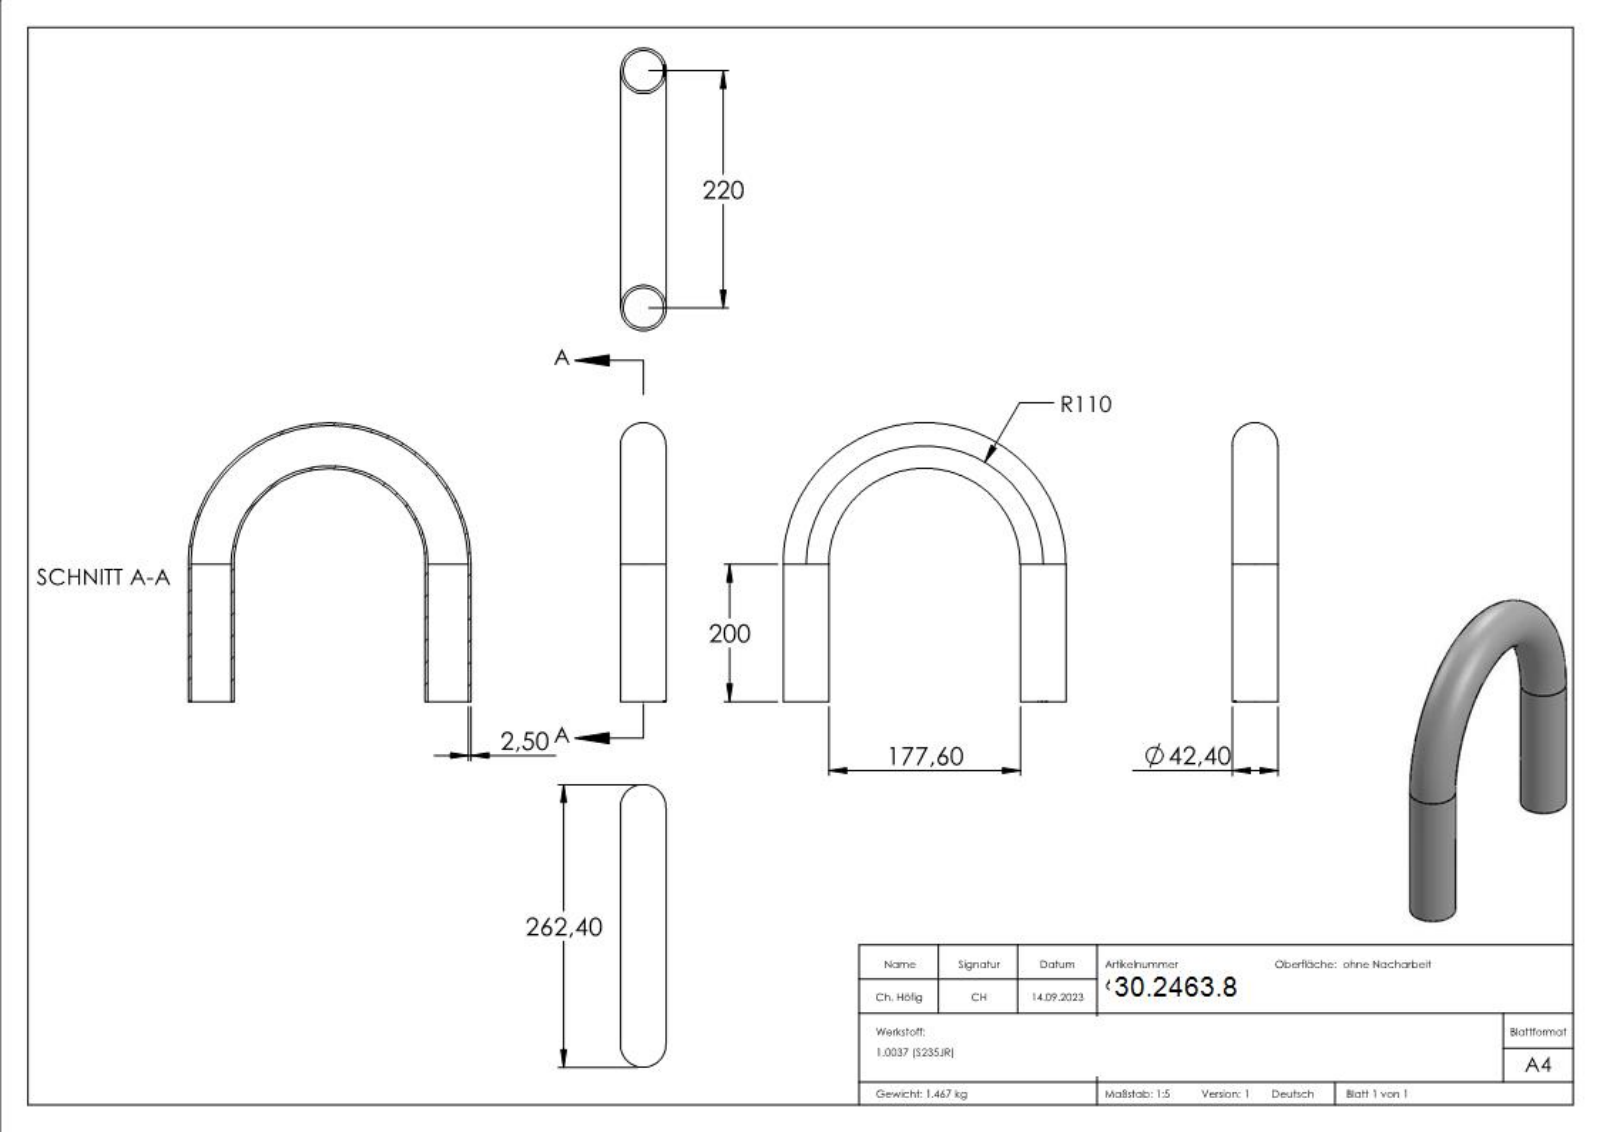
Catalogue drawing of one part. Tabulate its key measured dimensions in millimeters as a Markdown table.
| quantity | value |
| --- | --- |
| part name | 6967-U110 |
| STEP written by | SolidWorks 2018 (CONFIG_CONTROL_DESIGN) |
| units | millimeters |
| bodies | 1 solid, 214 faces (117 planar, 4 cylindrical, 93 other) |
| overall size | 262.4 × 258.41 × 42.4 |
| volume | 188 024 mm³ |
| surface area | 151 052 mm² |
| round holes (diameter × count) | 37.4 × 2 |
| round bosses / shafts (diameter × count) | 42.4 × 2 |
| main face-to-face distances | 0.44, 0.4, 0.36, 0.32, 0.47, 0.51, 0.39, 0.52, 0.79, 1.75 |
| hole center spacings | 220 |
